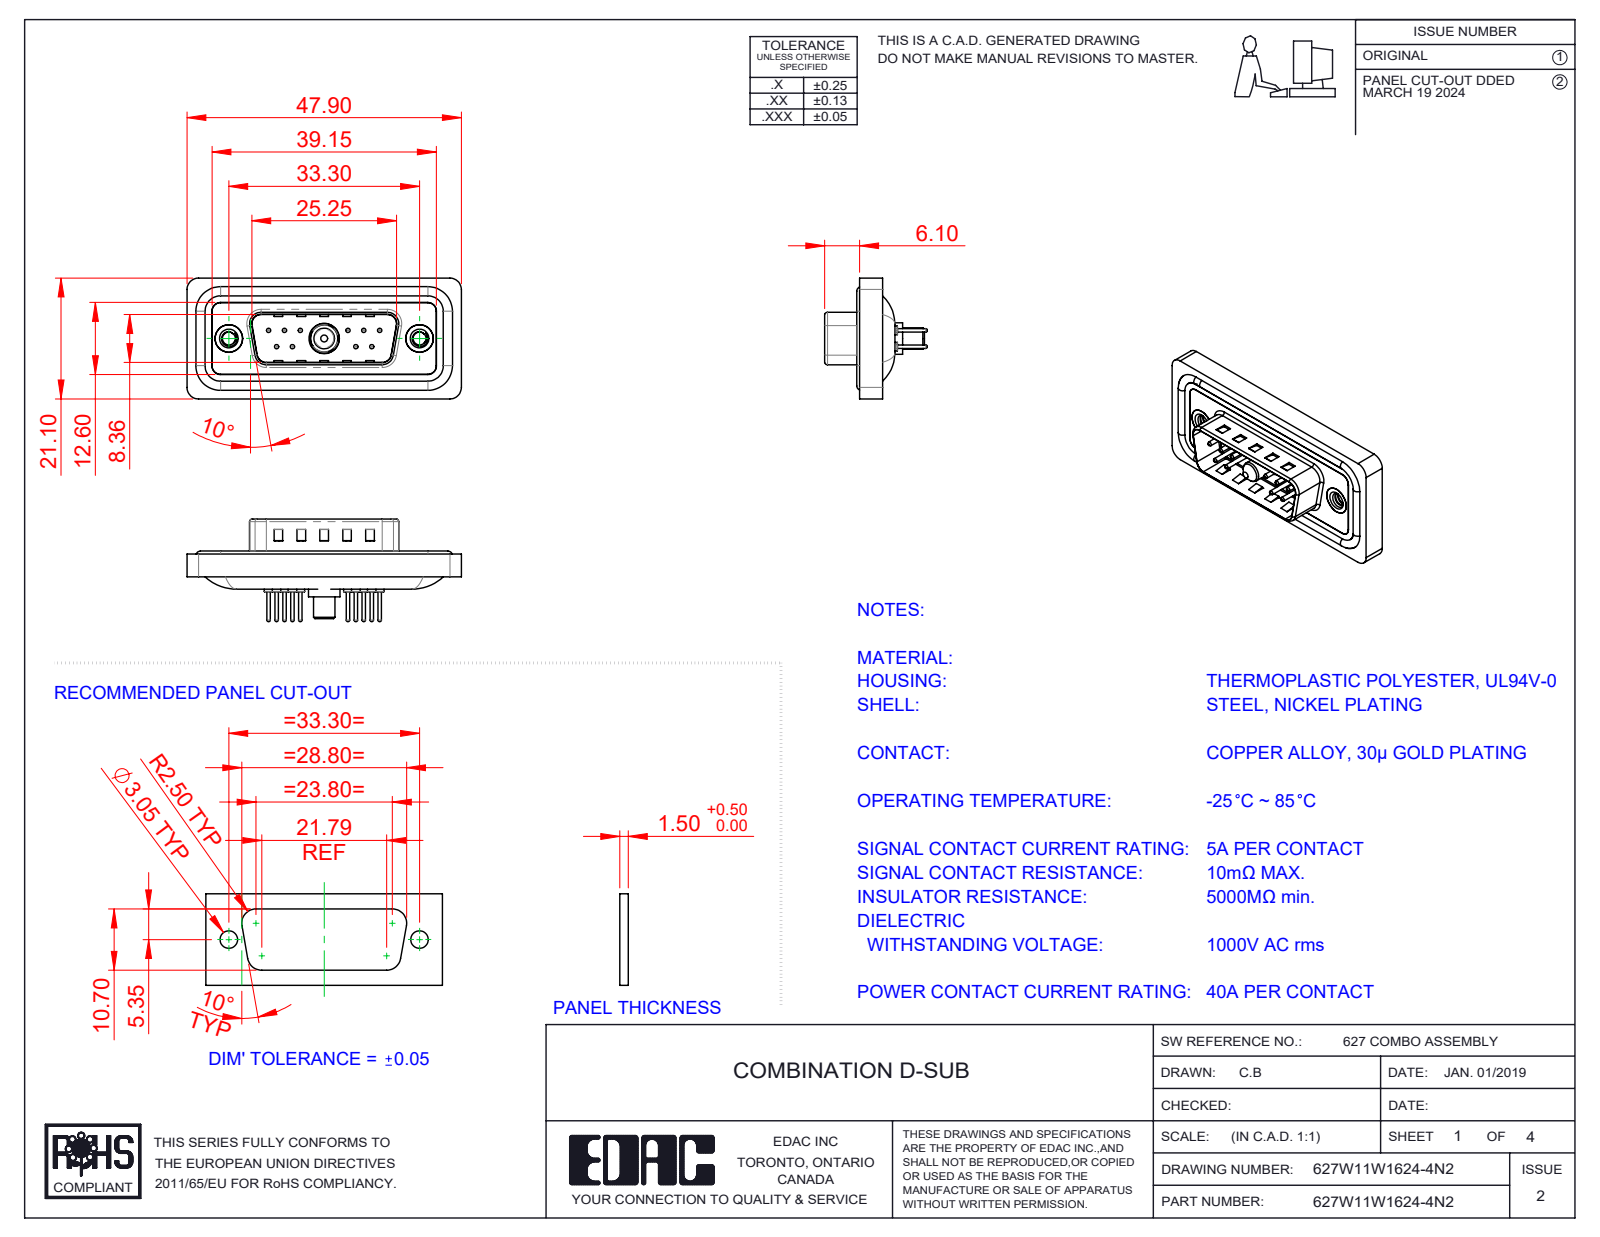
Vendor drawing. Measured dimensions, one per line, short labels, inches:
name: 627Combo Shell Front_15 Contacts; 627Combo Contact Row 2_24; 627Combo Housing_11W1; 627Combo Contact Row 1_24 (+5 more)
written by: SolidWorks 2023 (CONFIG_CONTROL_DESIGN)
unit: in
bodies: 19 solids, 869 faces (266 planar, 347 cylindrical, 256 other)
size: 1.886 × 0.831 × 0.705
volume: 0.334 in³; area: 13.71 in²
holes: 10× ⌀0.03, 10× ⌀0.063, 10× ⌀0.079, 2× ⌀0.089, 2× ⌀0.157, 2× ⌀0.189, 2× ⌀0.197, 1× ⌀0.191, 1× ⌀0.209
bosses: 10× ⌀0.059, 10× ⌀0.024, 4× ⌀0.063, 2× ⌀0.193, 1× ⌀0.217, 1× ⌀0.205, 1× ⌀0.187, 1× ⌀0.148
rounds: 26× R0.059, 20× R0.079, 8× R0.02, 8× R0.063, 7× R0.039, 4× R0.01, 4× R0.024, 4× R0.026
face distances: 0.016, 0.043, 0.063, 0.059, 0.02, 0.114, 0.122, 0.098, 0.161, 0.032
hole spacings: 0.124, 0.109, 0.545, 0.436, 0.654, 0.198, 0.198, 0.218
